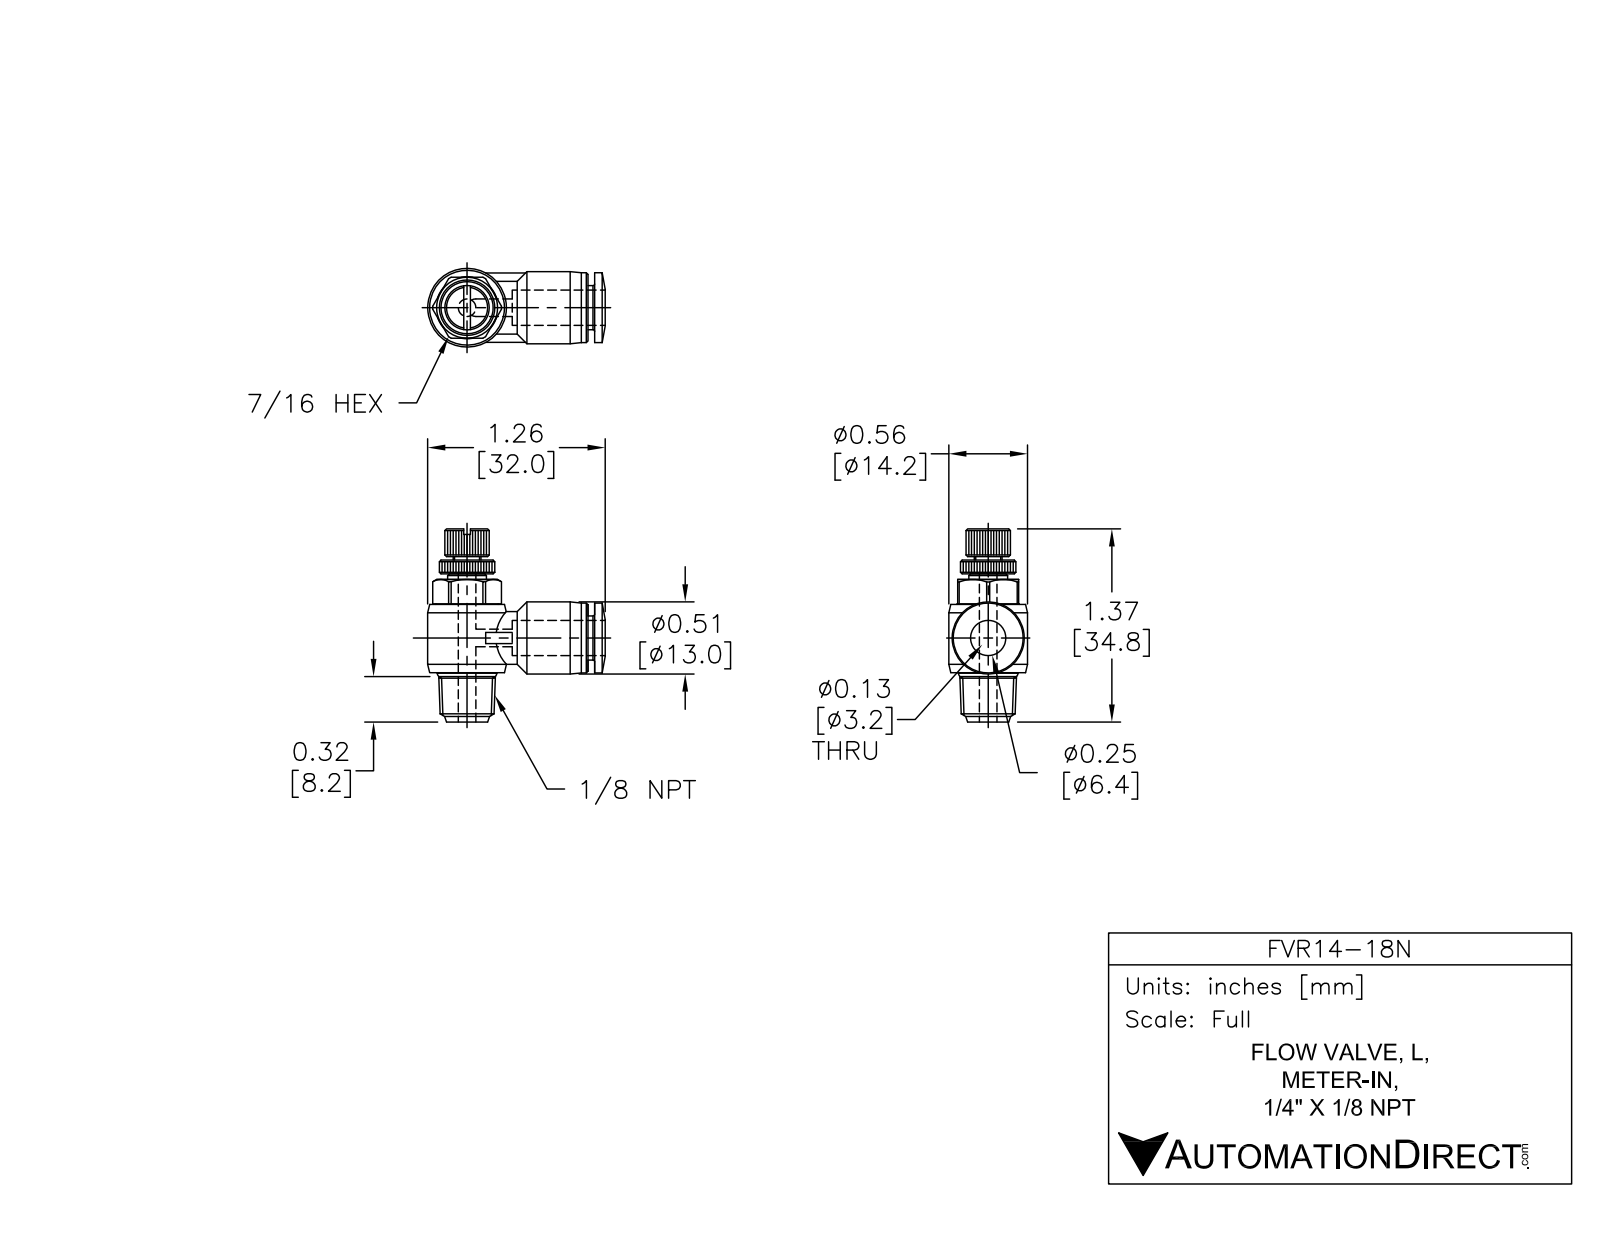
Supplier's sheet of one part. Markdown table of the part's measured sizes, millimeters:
| quantity | value |
| --- | --- |
| part name | FVR14-18N |
| STEP written by | SolidWorks 2015 (AUTOMOTIVE_DESIGN) |
| units | millimeters |
| bodies | 1 solid, 507 faces (198 planar, 113 cylindrical, 196 other) |
| overall size | 39.8 × 32 × 14.2 |
| volume | 4 980 mm³ |
| surface area | 3 251 mm² |
| round holes (diameter × count) | 3 × 2, 6.6 × 1 |
| round bosses / shafts (diameter × count) | 14.2 × 1, 13 × 1, 12.6 × 1, 11.2 × 1, 10.3 × 1, 9.5 × 1, 8 × 1, 7 × 1 |
| partial cylindrical surfaces (radius × count) | 4 × 1, 5 × 1, 6.2 × 1 |
| main face-to-face distances | 11, 1.2, 16.8, 5.2, 20.3, 3.5, 1, 12.3, 4.5, 8 |
